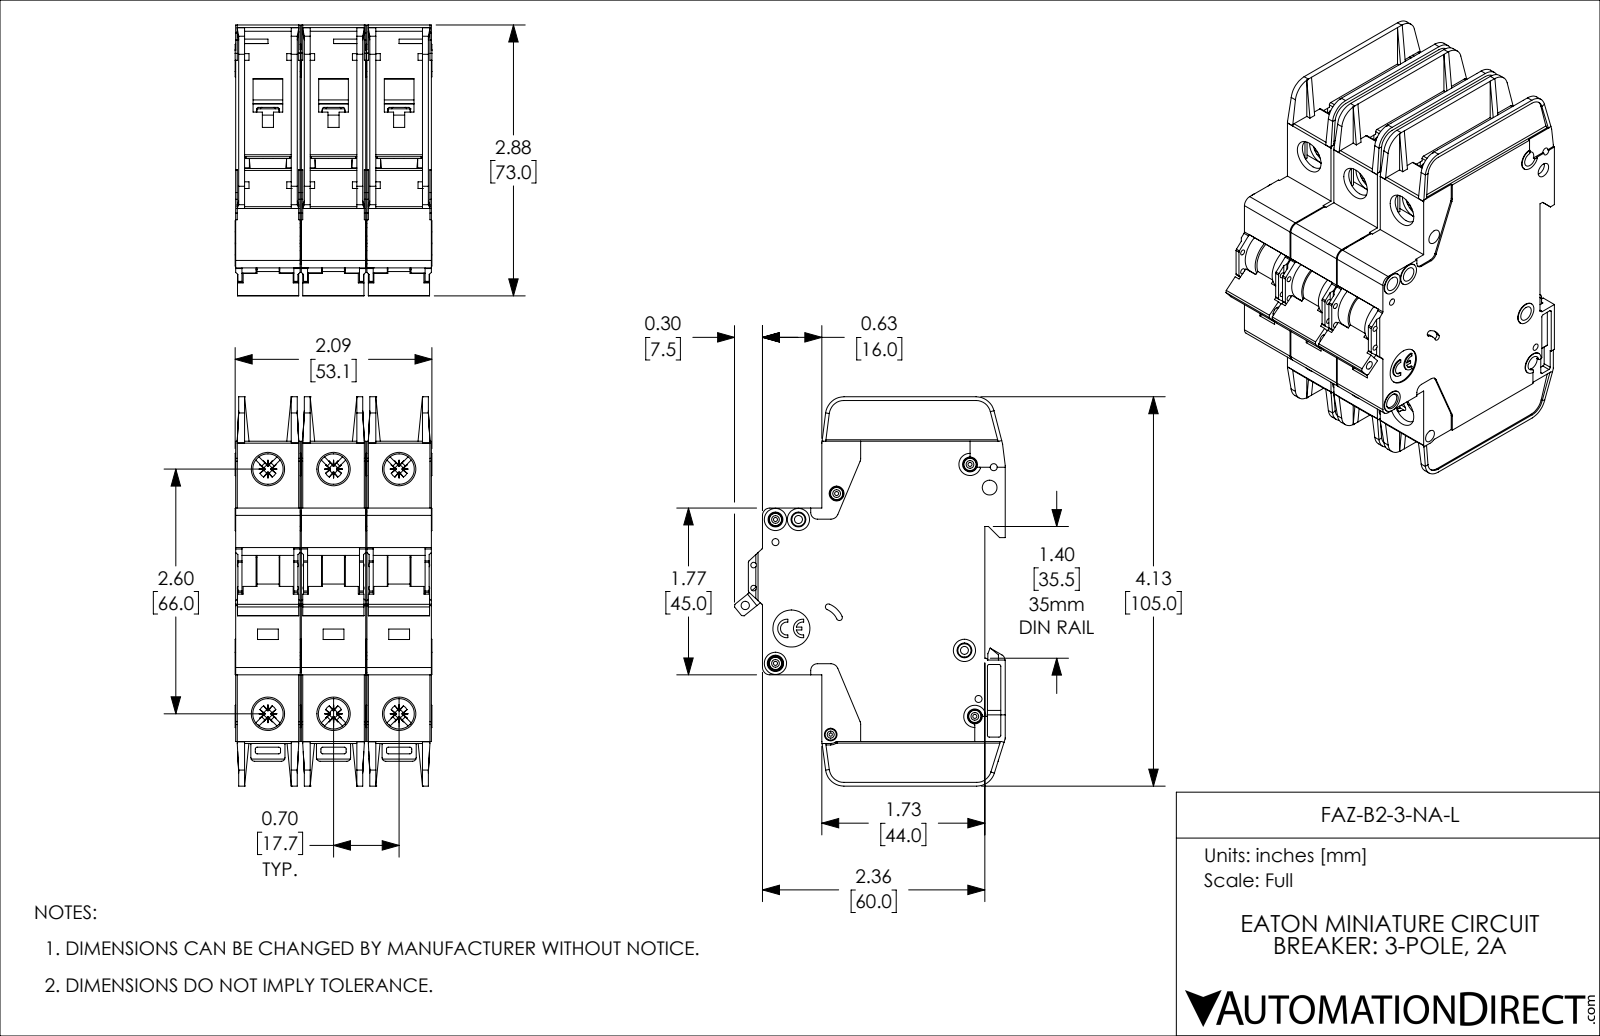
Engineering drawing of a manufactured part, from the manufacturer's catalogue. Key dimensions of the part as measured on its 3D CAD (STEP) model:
Part name (STEP PRODUCT): FAZ-B2-3-NA-L
STEP written by: SolidWorks 2019 (AUTOMOTIVE_DESIGN)
Units: inches
Bodies: 3 solids, 3381 faces (2013 planar, 1071 cylindrical, 297 other)
Overall size (bounding box): 4.134 × 2.876 × 2.091
Volume: 14.05 in³ · Surface area: 123 in²
Round holes (diameter × count): ⌀0.157 ×8, ⌀0.323 ×6, ⌀0.043 ×5, ⌀0.075 ×4, ⌀0.059 ×2, ⌀0.085 ×2, ⌀0.035 ×1, ⌀0.089 ×1, ⌀0.098 ×1, ⌀0.134 ×1, ⌀0.394 ×1
Round bosses / shafts (diameter × count): ⌀0.13 ×5, ⌀0.236 ×4, ⌀0.118 ×4, ⌀0.098 ×3
Partial cylindrical surfaces — rounded edges, fillets, slot ends (radius × count): R0.02 ×72, R0.016 ×30, R0.039 ×18, R0.043 ×12, R0.079 ×12, R0.008 ×6, R0.01 ×6, R0.028 ×6
Main face-to-face distances: 0.697, 0.047, 1.394, 0.685, 0.591, 1.382, 0.744, 0.65, 0.106, 0.094
Hole centre spacings: 0.697, 2.69, 2.598, 0.244, 0.537, 0.87, 1.394, 2.948
